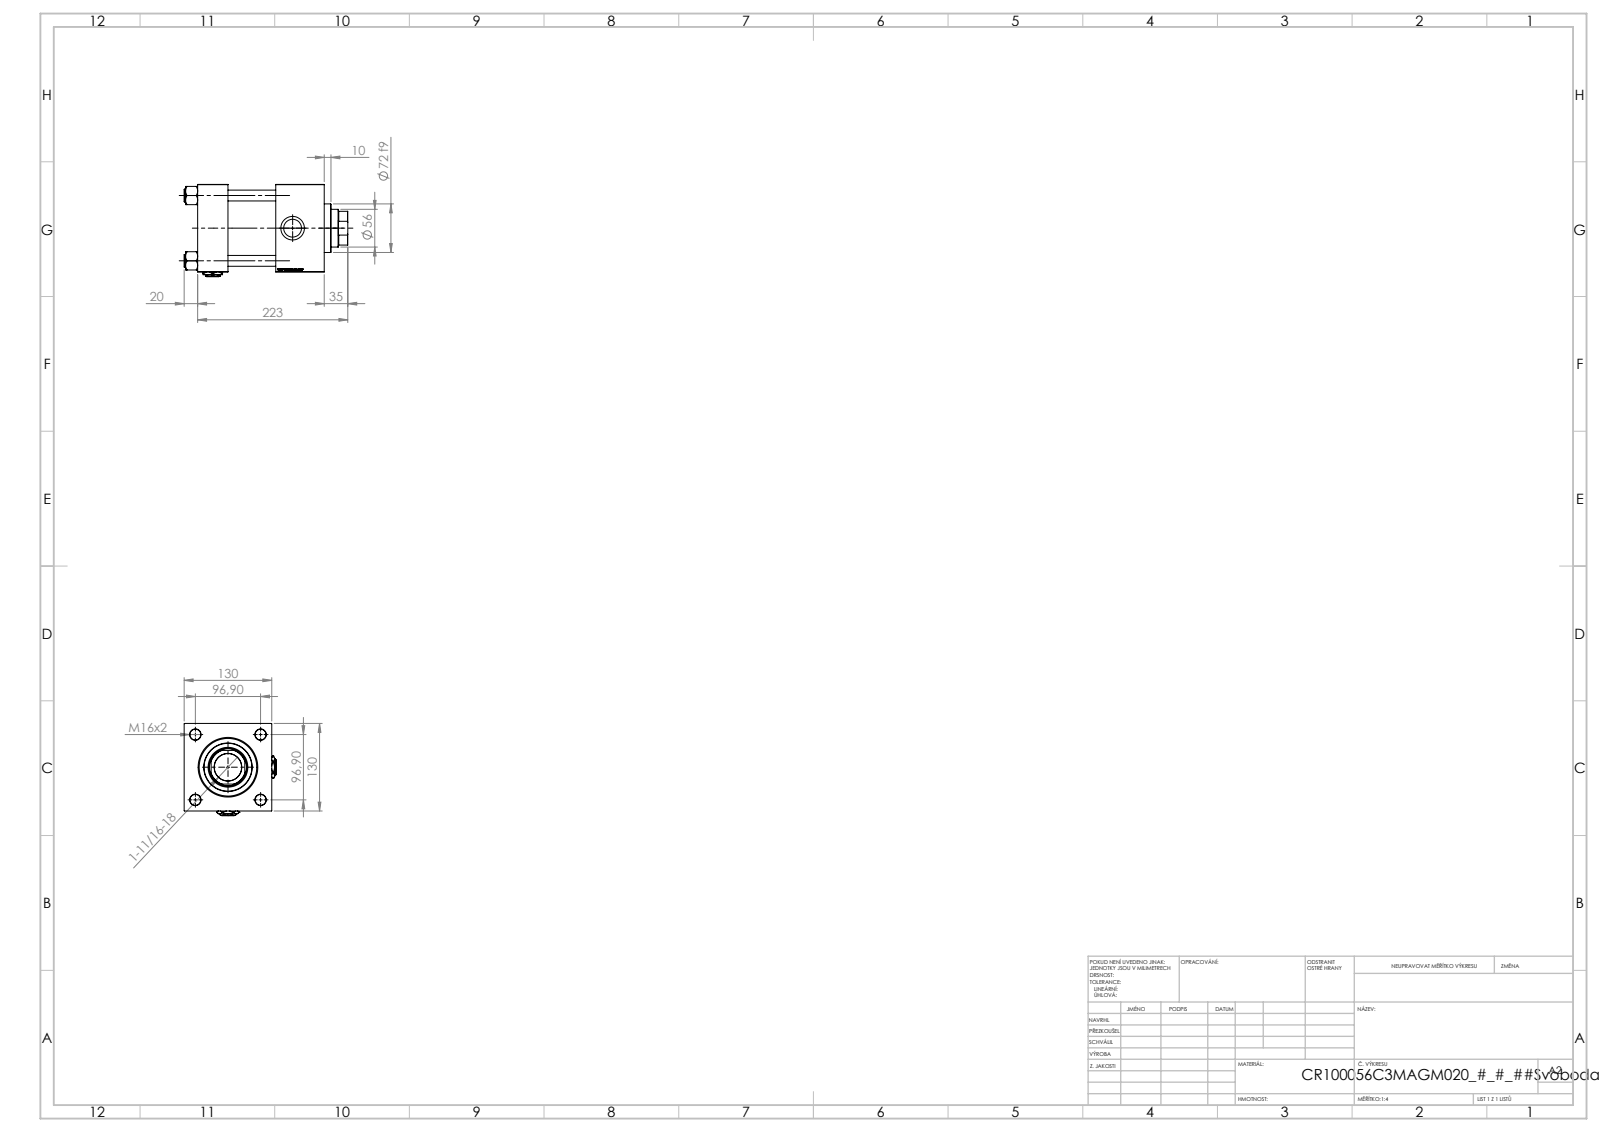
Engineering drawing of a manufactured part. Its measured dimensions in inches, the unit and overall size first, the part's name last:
Units: inches
Overall size (bounding box): 9.567 × 5.394 × 5.394
Round holes (diameter × count): ⌀0.63 ×4, ⌀0.276 ×2, ⌀1.041 ×2, ⌀1.378 ×2, ⌀1.594 ×1, ⌀2.205 ×1, ⌀2.323 ×1, ⌀2.992 ×1, ⌀3.366 ×1, ⌀3.937 ×1
Round bosses / shafts (diameter × count): ⌀0.748 ×4, ⌀4.173 ×1, ⌀2.835 ×1
Partial cylindrical surfaces — rounded edges, fillets, slot ends (radius × count): R1.063 ×1
Main face-to-face distances: 5.118, 1.772, 7.402, 5.63, 4.567, 2.795, 2.835, 0.787, 2.008, 3.622
Hole centre spacings: 2.698, 3.815, 5.395
Volume: 150.1 in³ · Surface area: 527.9 in²
Bodies: 13 solids, 1297 faces (621 planar, 98 cylindrical, 578 other)
Part name (STEP PRODUCT): NUT_M5_C; V215CR_C_TYCINKA; V215CR_VCP_C; V215CR_C_Body (+2 more)
STEP written by: SolidWorks 2019 (CONFIG_CONTROL_DESIGN)
